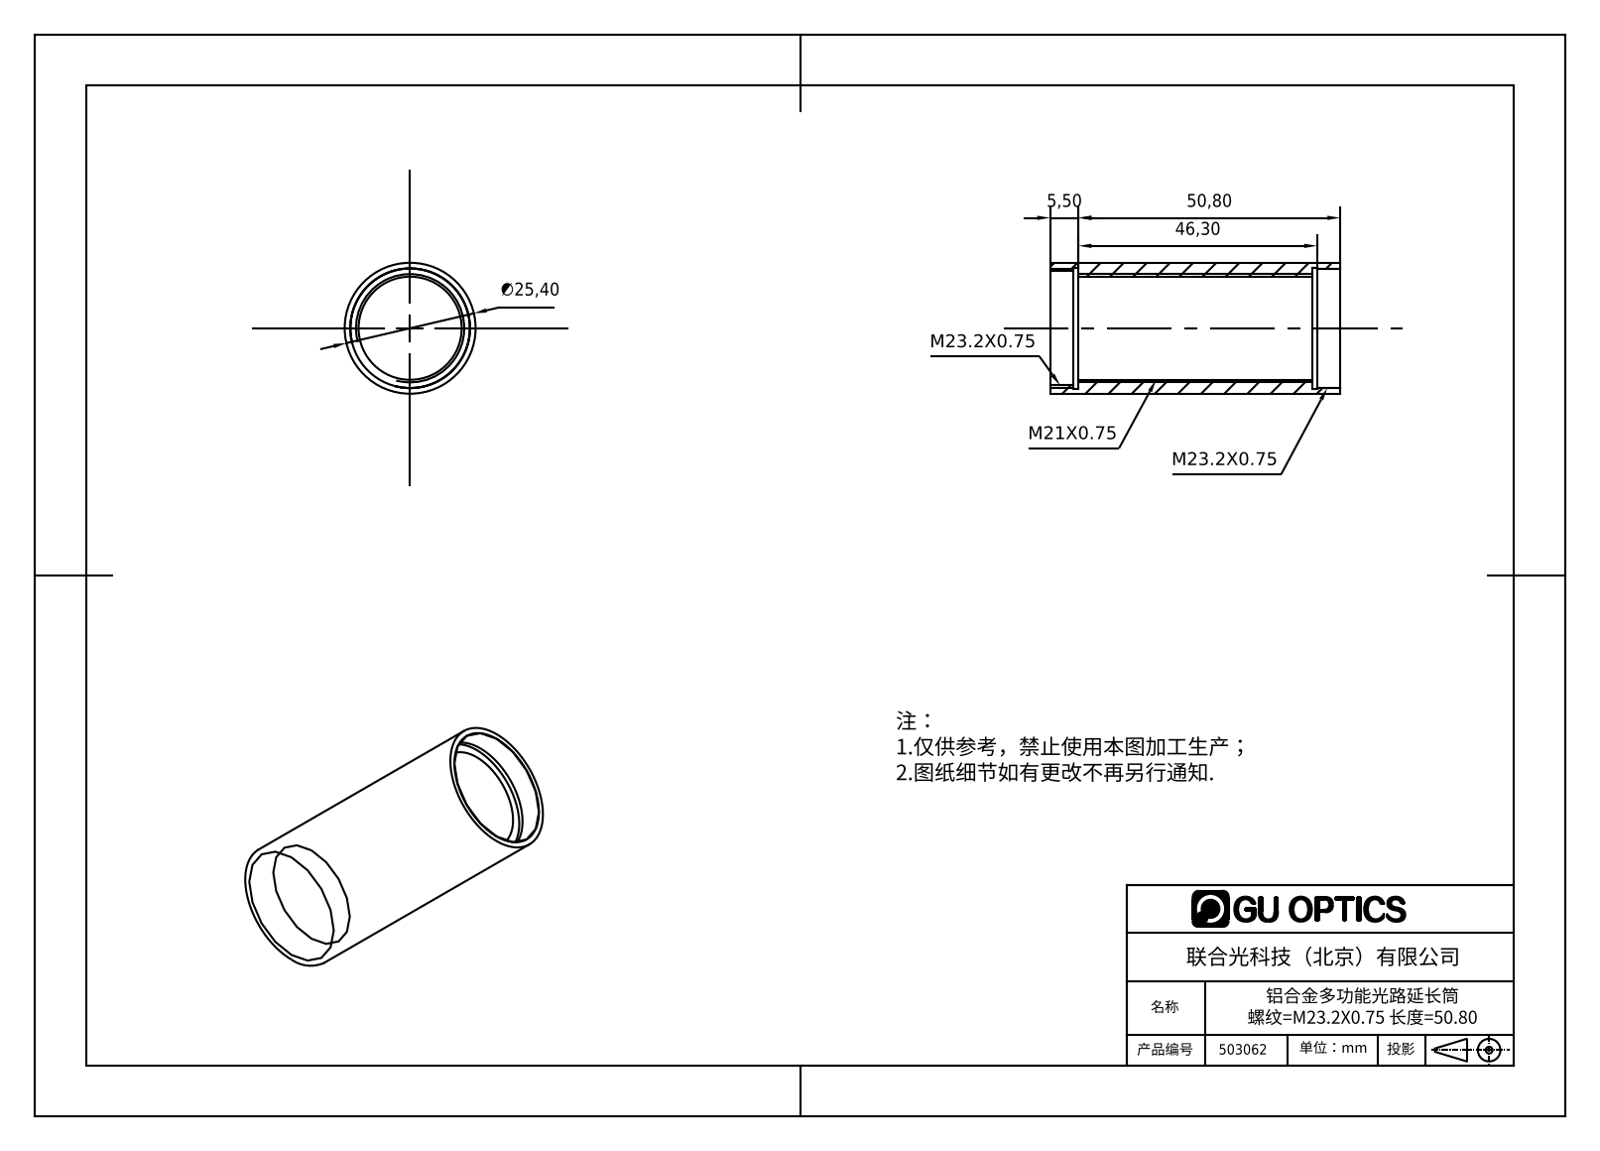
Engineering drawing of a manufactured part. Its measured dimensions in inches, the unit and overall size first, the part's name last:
Units: inches
Overall size (bounding box): 2.217 × 1 × 1
Round holes (diameter × count): ⌀0.787 ×1, ⌀0.874 ×1, ⌀0.913 ×1, ⌀0.921 ×1
Round bosses / shafts (diameter × count): ⌀1 ×1
Main face-to-face distances: 0.217, 2, 1.783, 2.217, 0.177, 2.039, 0.039, 1.823, 1.862
Volume: 0.598 in³ · Surface area: 13.35 in²
Bodies: 1 solid, 18 faces (6 planar, 12 cylindrical, 0 other)
Part name (STEP PRODUCT): 503062
STEP written by: SolidWorks 2016 (AUTOMOTIVE_DESIGN)
